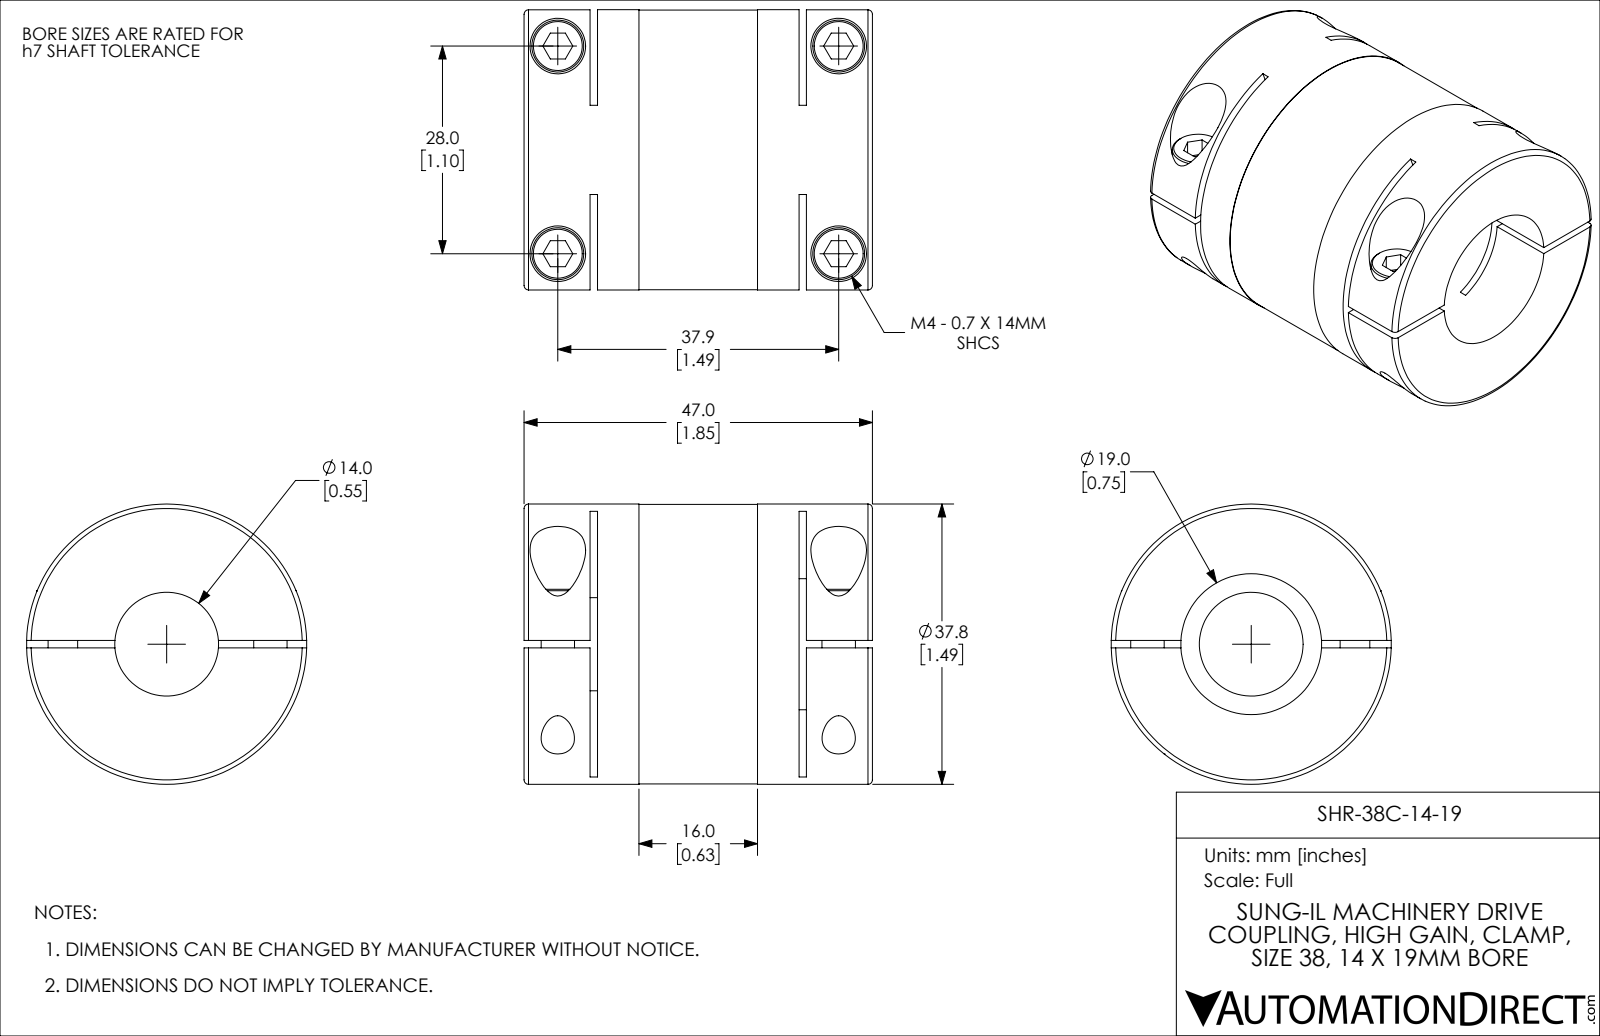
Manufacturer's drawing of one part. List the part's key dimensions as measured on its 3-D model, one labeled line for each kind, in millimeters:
Part name (STEP PRODUCT): SHR-38C-14-19
STEP written by: SolidWorks 2021 (CONFIG_CONTROL_DESIGN)
Units: millimetres
Bodies: 1 solid, 144 faces (70 planar, 58 cylindrical, 16 other)
Overall size (bounding box): 47 × 37.8 × 37.8
Volume: 37 223 mm³ · Surface area: 15 371 mm²
Round holes (diameter × count): ⌀4.5 ×4, ⌀7.5 ×4, ⌀14 ×1, ⌀19 ×1, ⌀21 ×1
Round bosses / shafts (diameter × count): ⌀7 ×4, ⌀4 ×2, ⌀37.8 ×1, ⌀37.7 ×1
Partial cylindrical surfaces — rounded edges, fillets, slot ends (radius × count): R50 ×2
Main face-to-face distances: 1, 9.9, 37.1, 8.9, 38.1, 28.2, 47, 27.2, 29.2, 31.5
Hole centre spacings: 28, 37.9, 47.12
